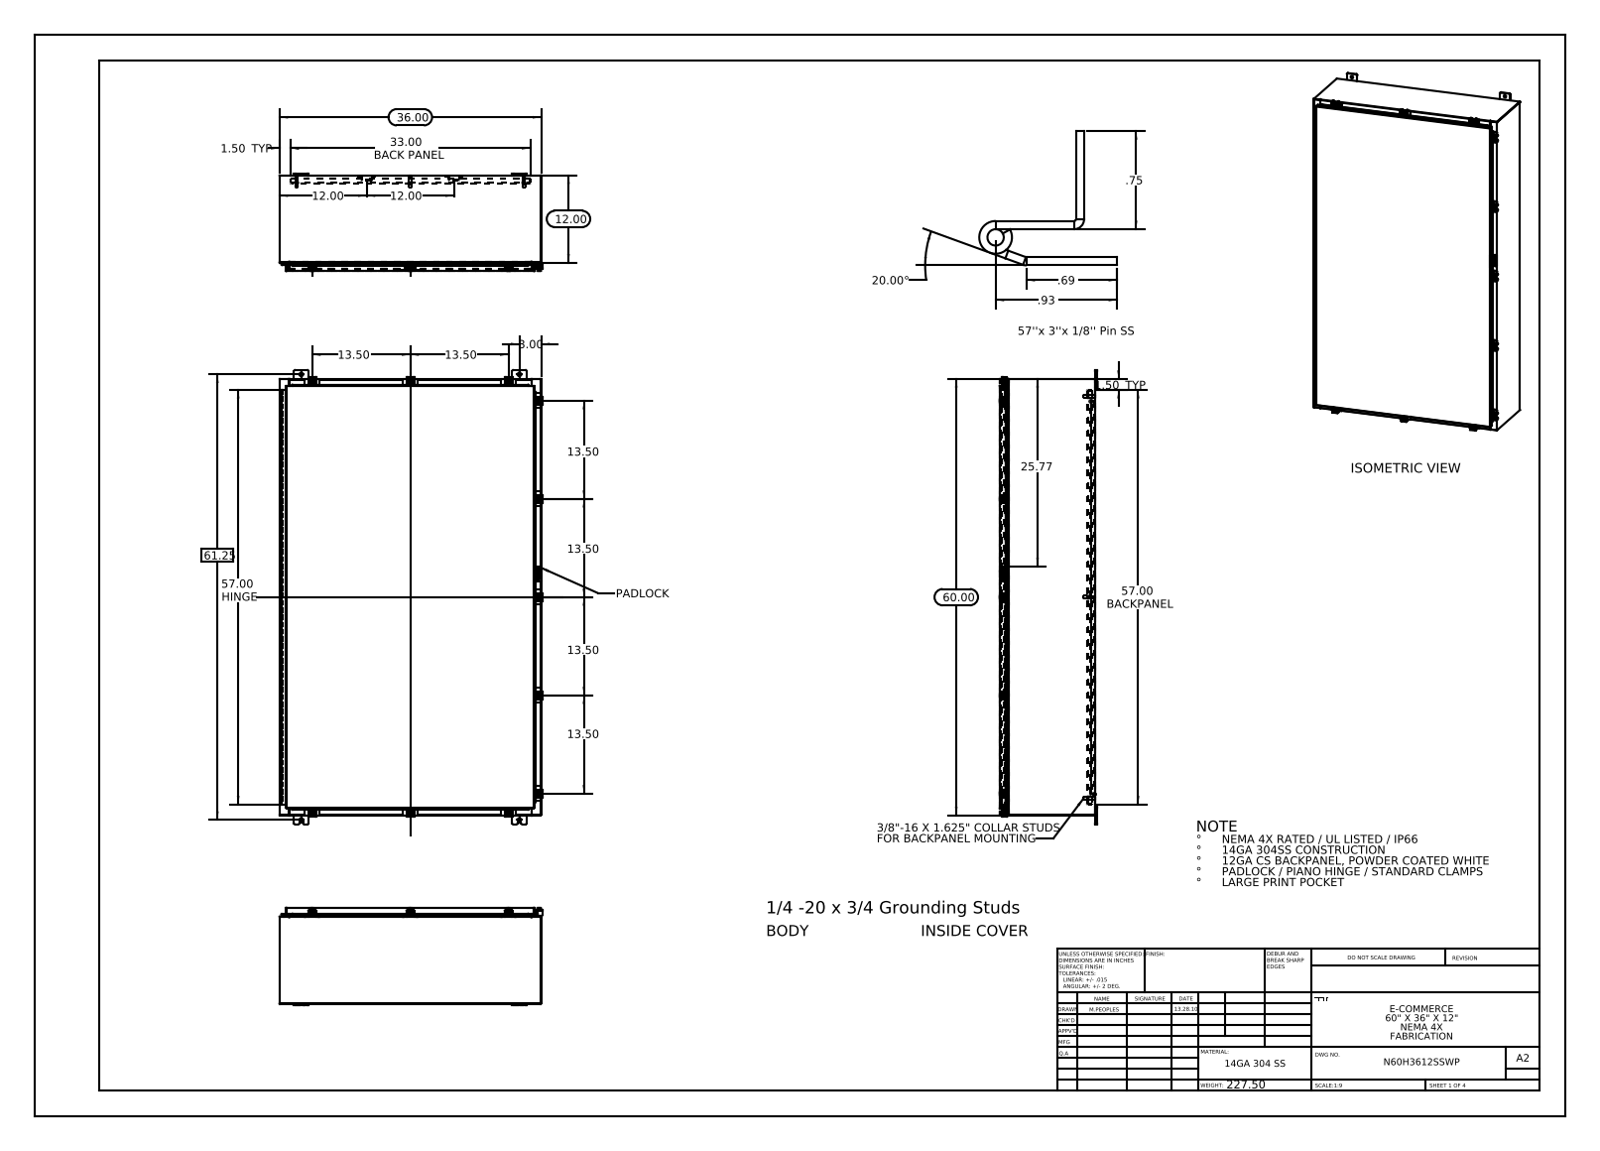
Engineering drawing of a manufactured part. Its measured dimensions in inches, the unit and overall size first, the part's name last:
Units: inches
Overall size (bounding box): 62.5 × 36.211 × 13.389
Round holes (diameter × count): ⌀0.5 ×12, ⌀0.213 ×11, ⌀0.26 ×11, ⌀0.25 ×8, ⌀0.125 ×2, ⌀0.125 ×1
Round bosses / shafts (diameter × count): ⌀0.25 ×12, ⌀0.5 ×11, ⌀0.399 ×11, ⌀0.625 ×8, ⌀0.375 ×8, ⌀0.33 ×8
Partial cylindrical surfaces — rounded edges, fillets, slot ends (radius × count): R0.06 ×50, R0.013 ×39, R0.088 ×33, R0.19 ×24, R0.12 ×22, R0.141 ×22, R0.05 ×17, R0.08 ×16
Main face-to-face distances: 0.075, 13.126, 13.051, 0.104, 13.201, 1, 12.126, 1.075, 12.051, 1.179
Hole centre spacings: 13.5, 13.663, 2.225, 27, 27.625, 29.802, 41.709, 57.39
Volume: 796 in³ · Surface area: 19 851 in²
Bodies: 79 solids, 3408 faces (1766 planar, 1466 cylindrical, 176 other)
Part name (STEP PRODUCT): N60H3612SSWP Enclosure Stiffener; N60H3612SSWP Hinge Enclosure Side2; N60H3612SSWP Clamp Bracket; N60H3612SSWP Body (+8 more)
STEP written by: SolidWorks 2013 (CONFIG_CONTROL_DESIGN)
